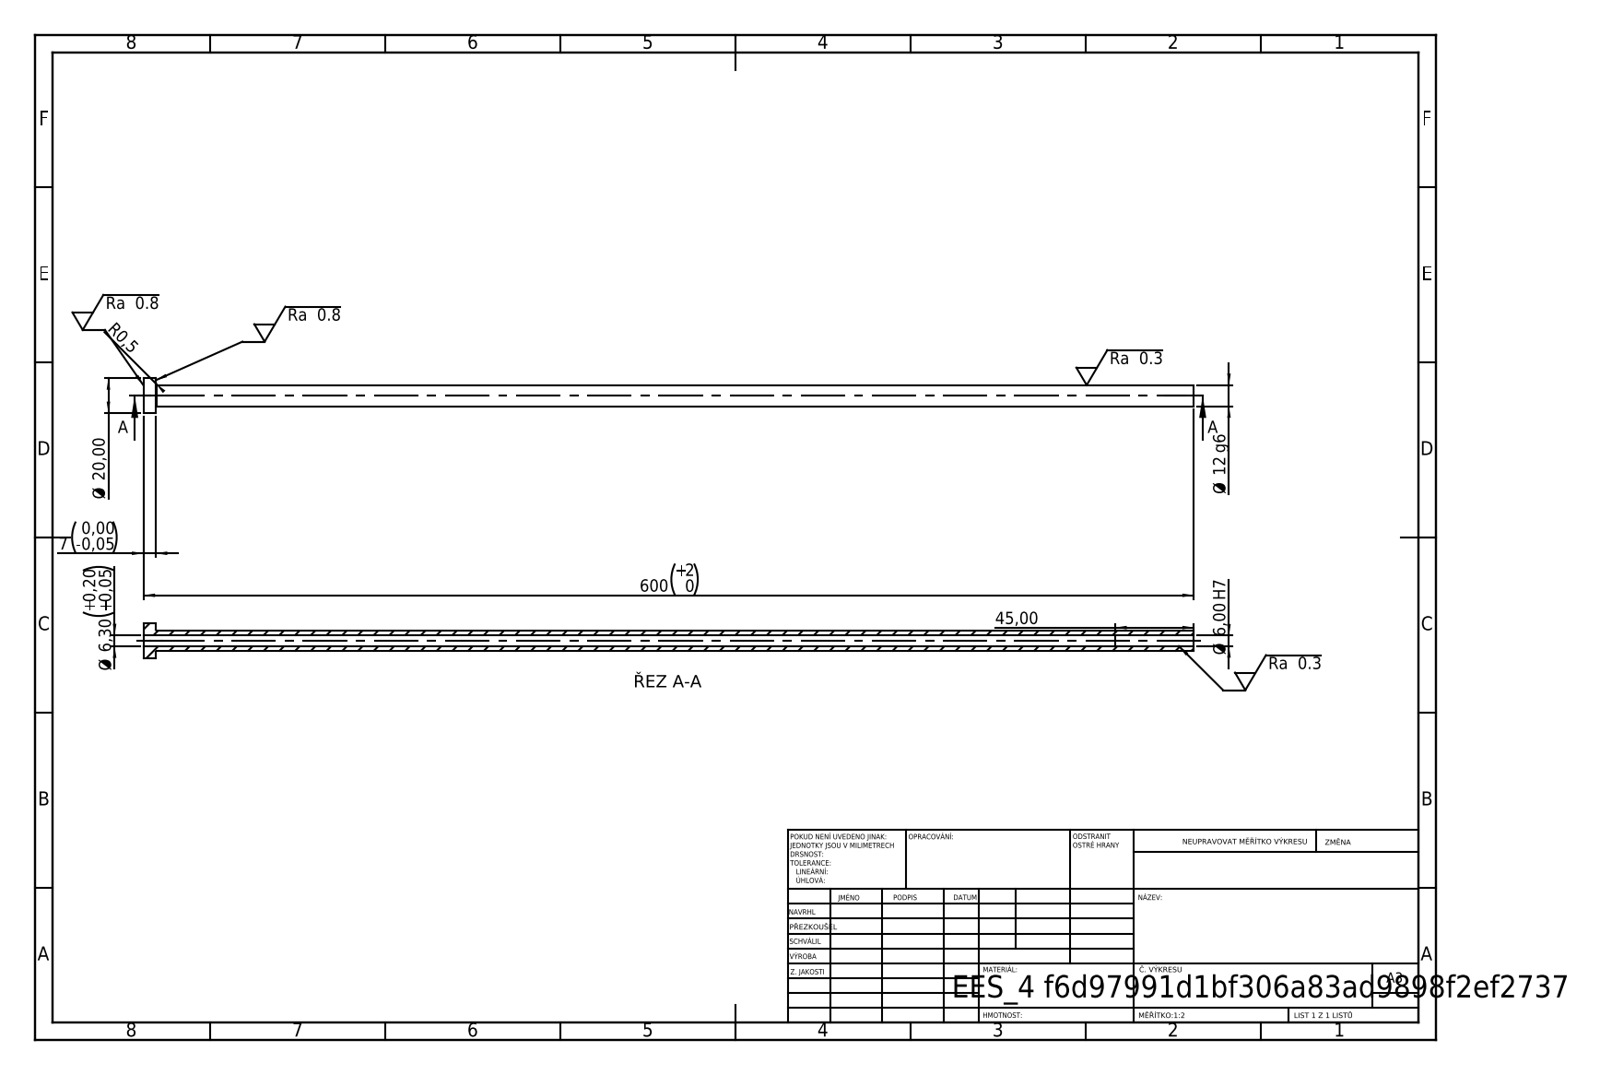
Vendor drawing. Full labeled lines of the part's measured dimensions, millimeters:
STEP written by: SolidWorks 2019 (CONFIG_CONTROL_DESIGN)
Units: millimetres
Bodies: 1 solid, 14 faces (4 planar, 8 cylindrical, 2 other)
Overall size (bounding box): 600 × 20 × 20
Volume: 50 695 mm³ · Surface area: 35 192 mm²
Round holes (diameter × count): ⌀6 ×1, ⌀6.3 ×1
Round bosses / shafts (diameter × count): ⌀20 ×1, ⌀12 ×1
Main face-to-face distances: 7, 600, 593, 555, 548, 45
